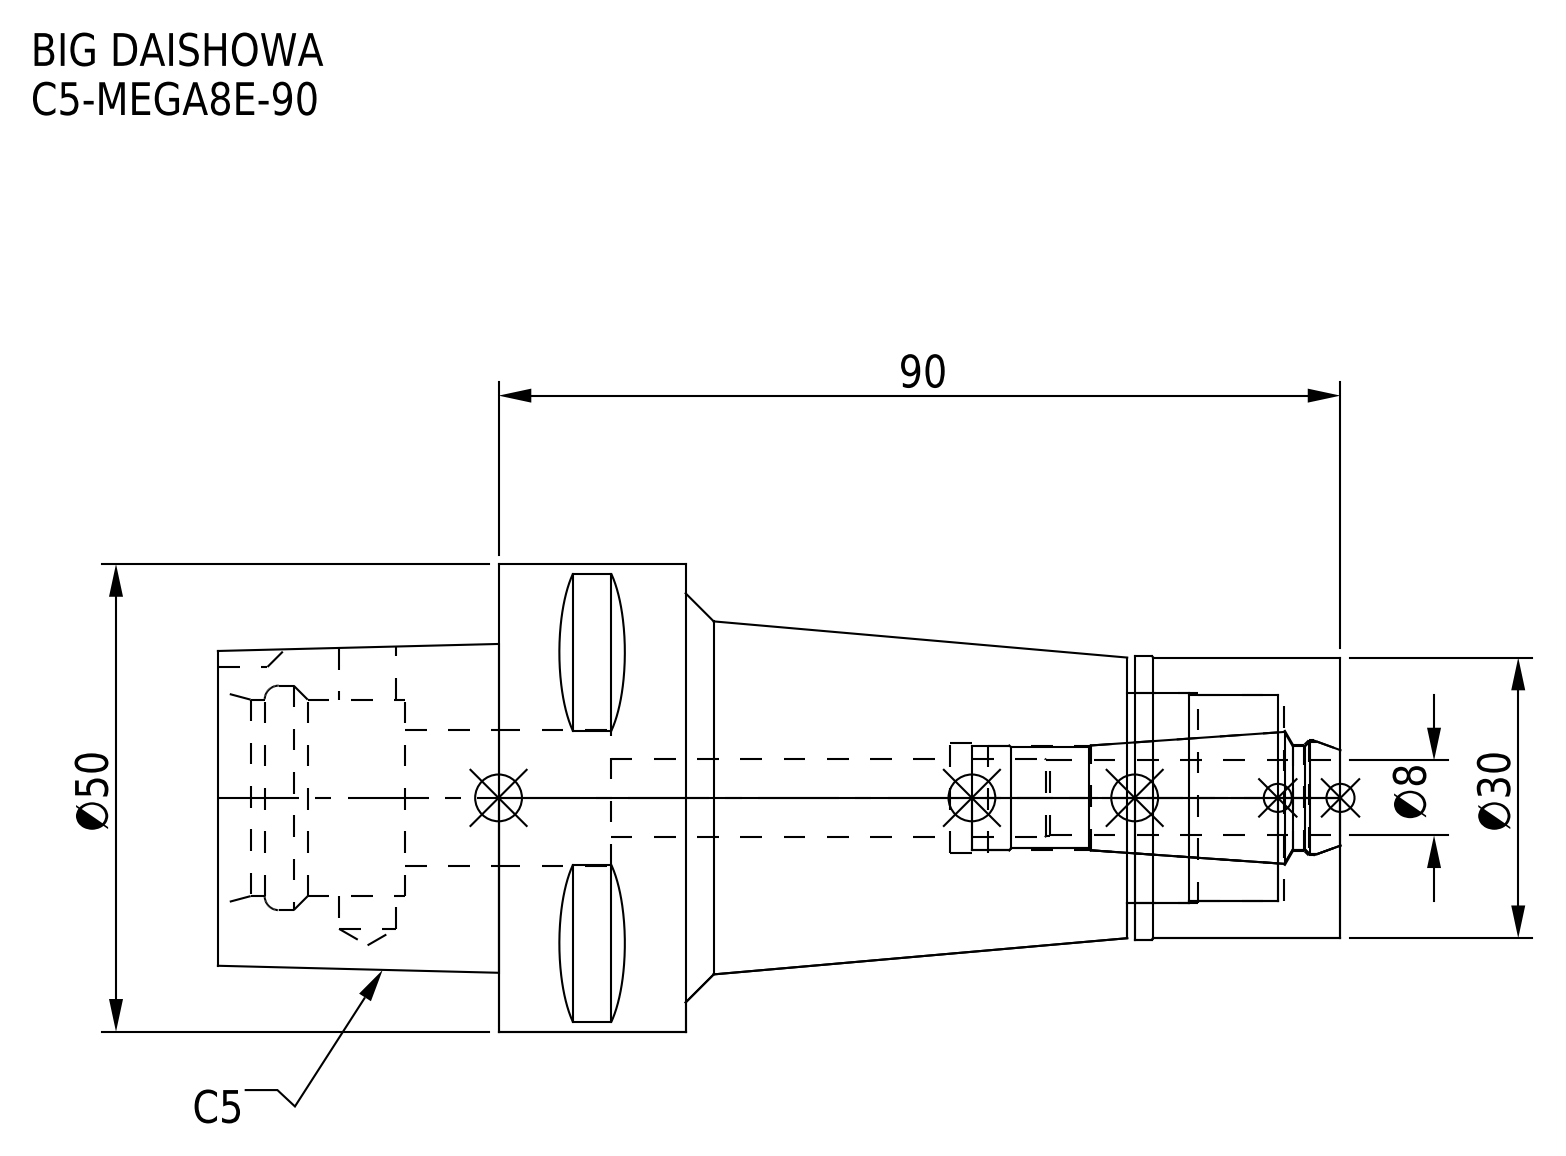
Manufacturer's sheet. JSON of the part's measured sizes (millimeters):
{"part_name": "C5-MEGA8E-90; C5-MEGA8E-90-080-FreeParts; C5-MEGA8E-90-080.stp; C5-MEGA8E-90-080_ASM.stp (+3 more)", "step_written_by": "SolidWorks 2019 (CONFIG_CONTROL_DESIGN)", "units": "millimeters", "bodies": {"solids": 2, "faces": 97, "planar": 36, "cylindrical": 37, "other": 24}, "overall_size": [120, 50, 50], "volume_mm3": 107329, "surface_area_mm2": 25354, "round_holes": [[6.1, 1], [8.4, 1], [11.2, 1], [11.4, 1], [11.8, 1], [12.3, 1], [14.5, 1], [21, 1], [22, 1], [22.5, 1], [24, 1]], "round_bosses_or_shafts": [[50, 1], [30.3, 1], [30, 1]], "partial_cylinders_radius": [[4, 1]], "face_to_face_distances": [20, 90, 30, 70, 22, 120, 50, 48, 68, 98]}
